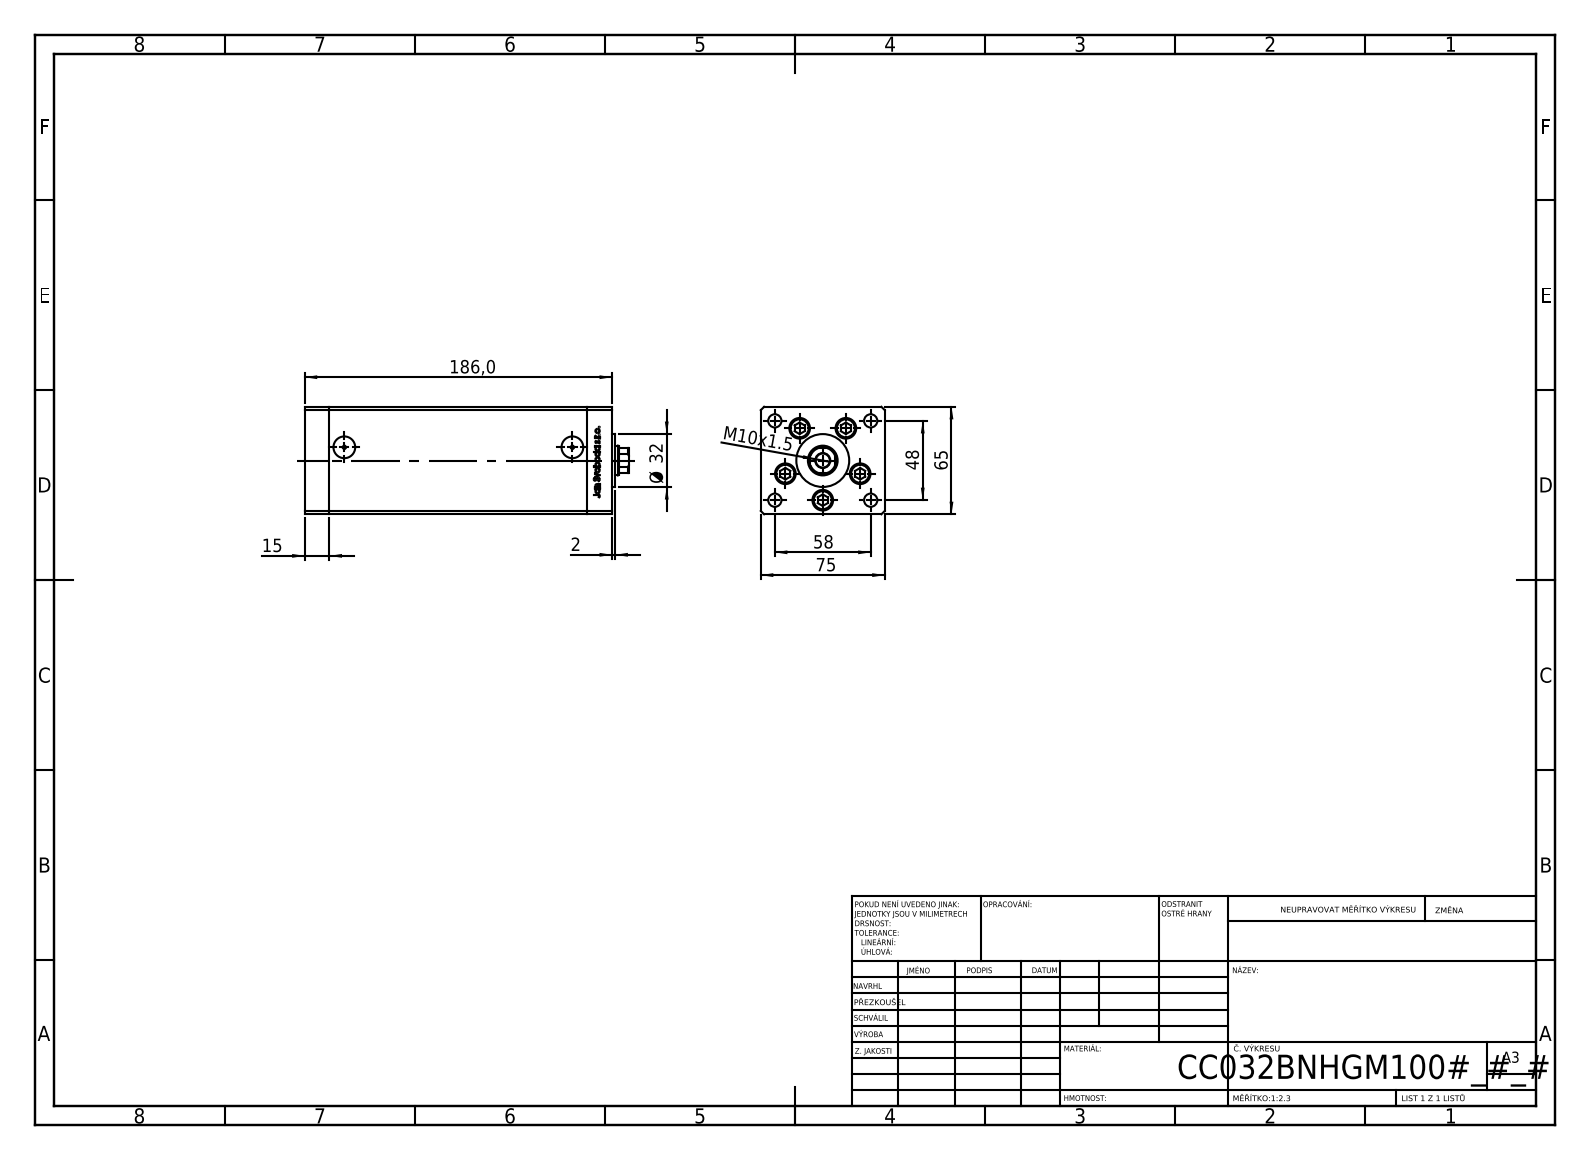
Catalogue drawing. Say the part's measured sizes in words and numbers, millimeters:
The part is named "V220C BACK_B; V220C_VC_B; V220C_B MIDDLE; ALLEN BOLT (+1 more)". Its 3-D file was written by "SolidWorks 2019 (CONFIG_CONTROL_DESIGN)". It is 14 solids with 1183 faces: 462 planar, 147 cylindrical and 574 other. Overall it measures 196 by 75 by 65 millimeters. Its volume is 804 986 cubic millimeters and its surface area 136 487 square millimeters. Round holes: 5 of diameter 9, 5 of diameter 12.5, 4 of diameter 8, 2 of diameter 2, 2 of diameter 13.16, 1 of diameter 8.5, 1 of diameter 18. Round bosses or shafts: 5 of diameter 8, 1 of diameter 32. Partial cylindrical surfaces (rounded edges, fillets, slot ends): 2 of radius 0.93, 1 of radius 8.5. The main face-to-face distances are 75, 65, 15, 156, 171, 186, 28, 54.5, 10.5, 26.25. The hole center spacings are 24, 37.64, 15.67, 17.22, 27.71, 28.83, 29, 32.63.
